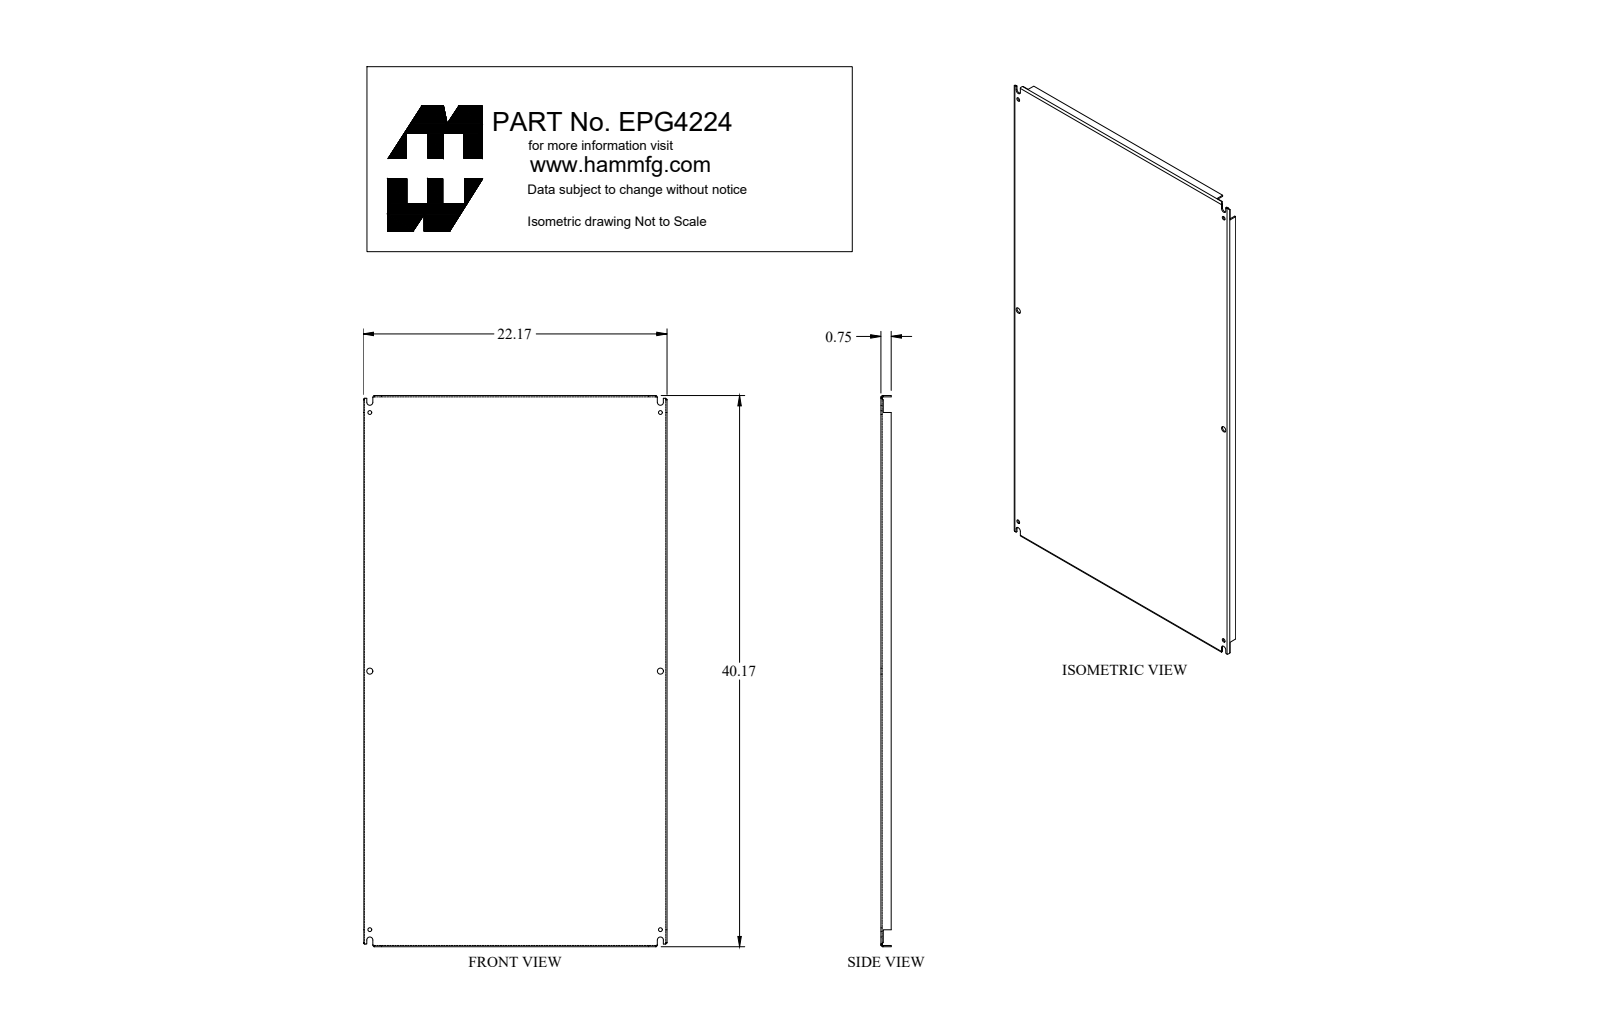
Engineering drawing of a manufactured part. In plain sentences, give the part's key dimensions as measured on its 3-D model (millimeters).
The part is named "EPG4224". Its 3-D file was written by "SolidWorks 2018 (AUTOMOTIVE_DESIGN)". It is 1 solid with 132 faces: 74 planar, 42 cylindrical and 16 other. Overall it measures 1020.3 by 563.1 by 19.1 millimeters. Its volume is 1 493 000 cubic millimeters and its surface area 1 246 000 square millimeters. Round holes: 4 of diameter 7.1, 2 of diameter 11.1. Partial cylindrical surfaces (rounded edges, fillets, slot ends): 4 of radius 1.2, 4 of radius 1.6, 4 of radius 3.6, 4 of radius 5.6. The main face-to-face distances are 2.4, 560.7, 1017.9, 563.1, 558.3, 1015.5, 1020.3, 19.1, 16.6, 4.3. The hole center spacings are 478.6, 720.2, 538.2, 957.3, 1098.2.
